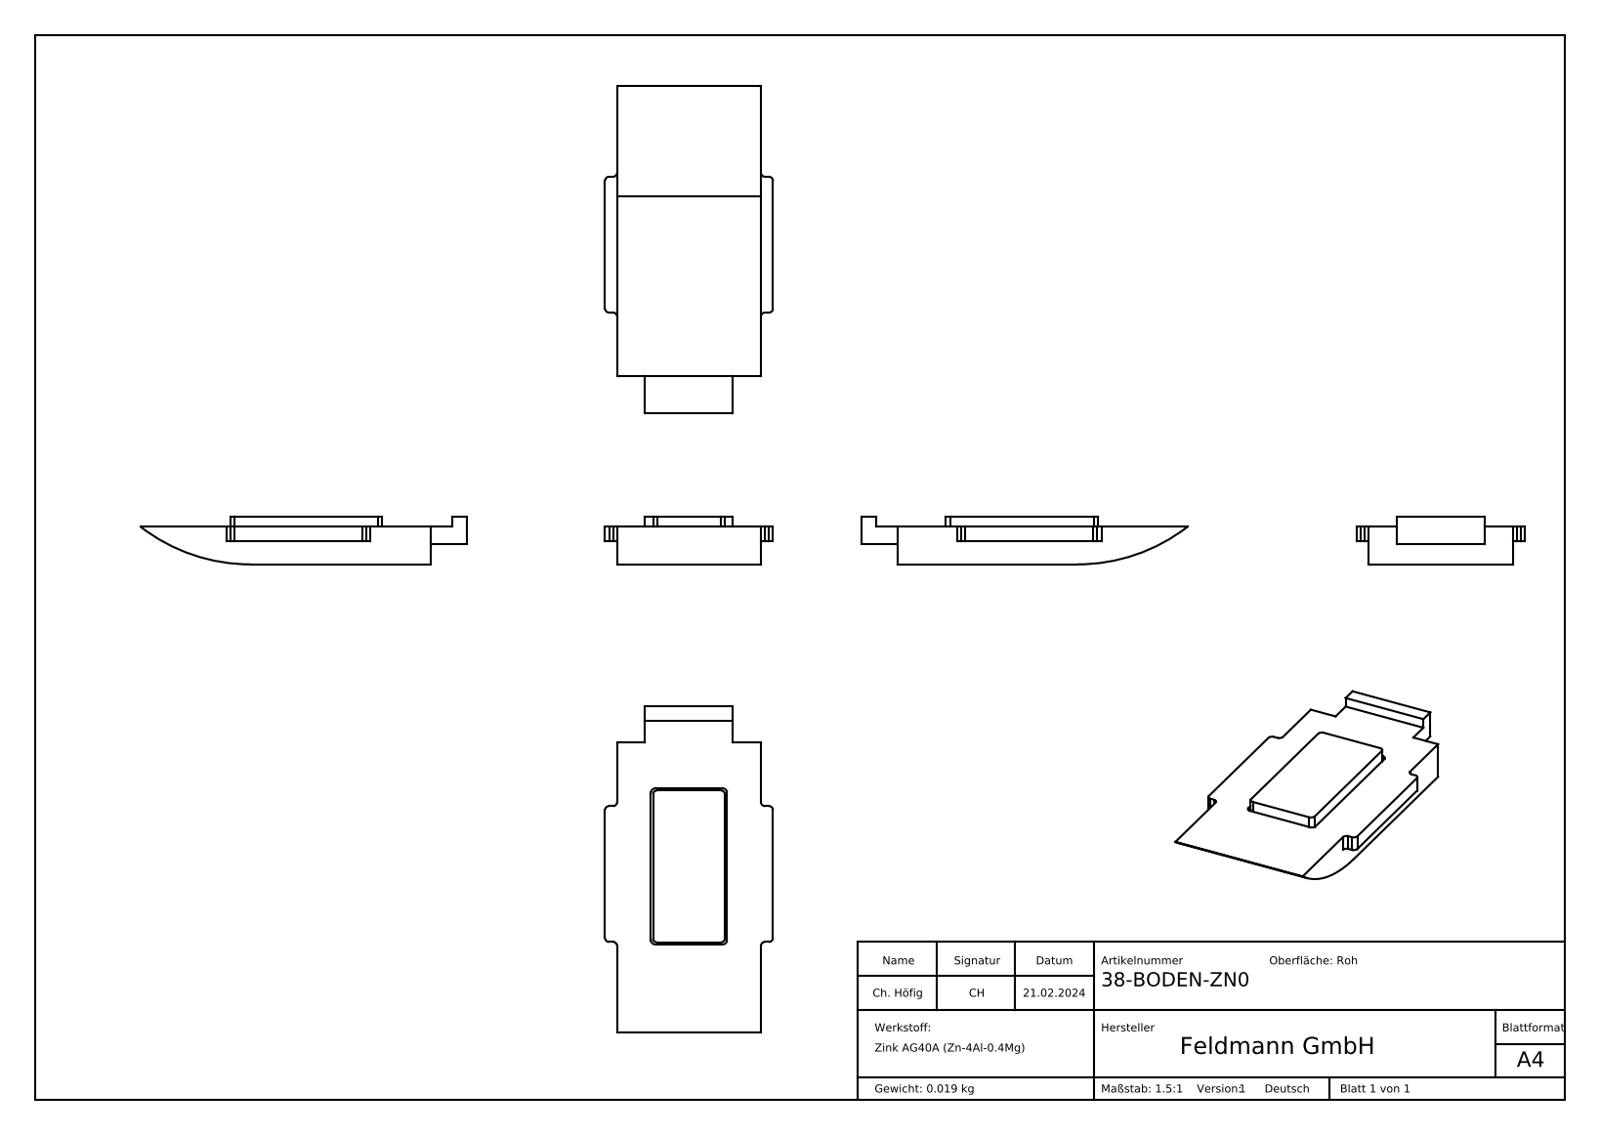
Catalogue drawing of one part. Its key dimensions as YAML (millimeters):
part_name: "38-Boden-GU_38-BODEN-ZN0-GU; 38-BODEN-ZN0; 38-Boden-XXX-OG_38-BODEN-ZN0 Teil1"
step_written_by: "SolidWorks 2018 (CONFIG_CONTROL_DESIGN)"
units: millimeters
bodies: {solids: 2, faces: 353, planar: 204, cylindrical: 17, other: 132}
overall_size: [40.85, 21, 6]
volume: 3169
surface_area: 2451
partial_cylinders:
  - {radius: 0.5, count: 16}
  - {radius: 22.5, count: 1}
face_to_face_distances: [4.75, 4.25, 0.5, 6, 1.75, 1.25, 18, 3.5, 1.85, 19.5]
